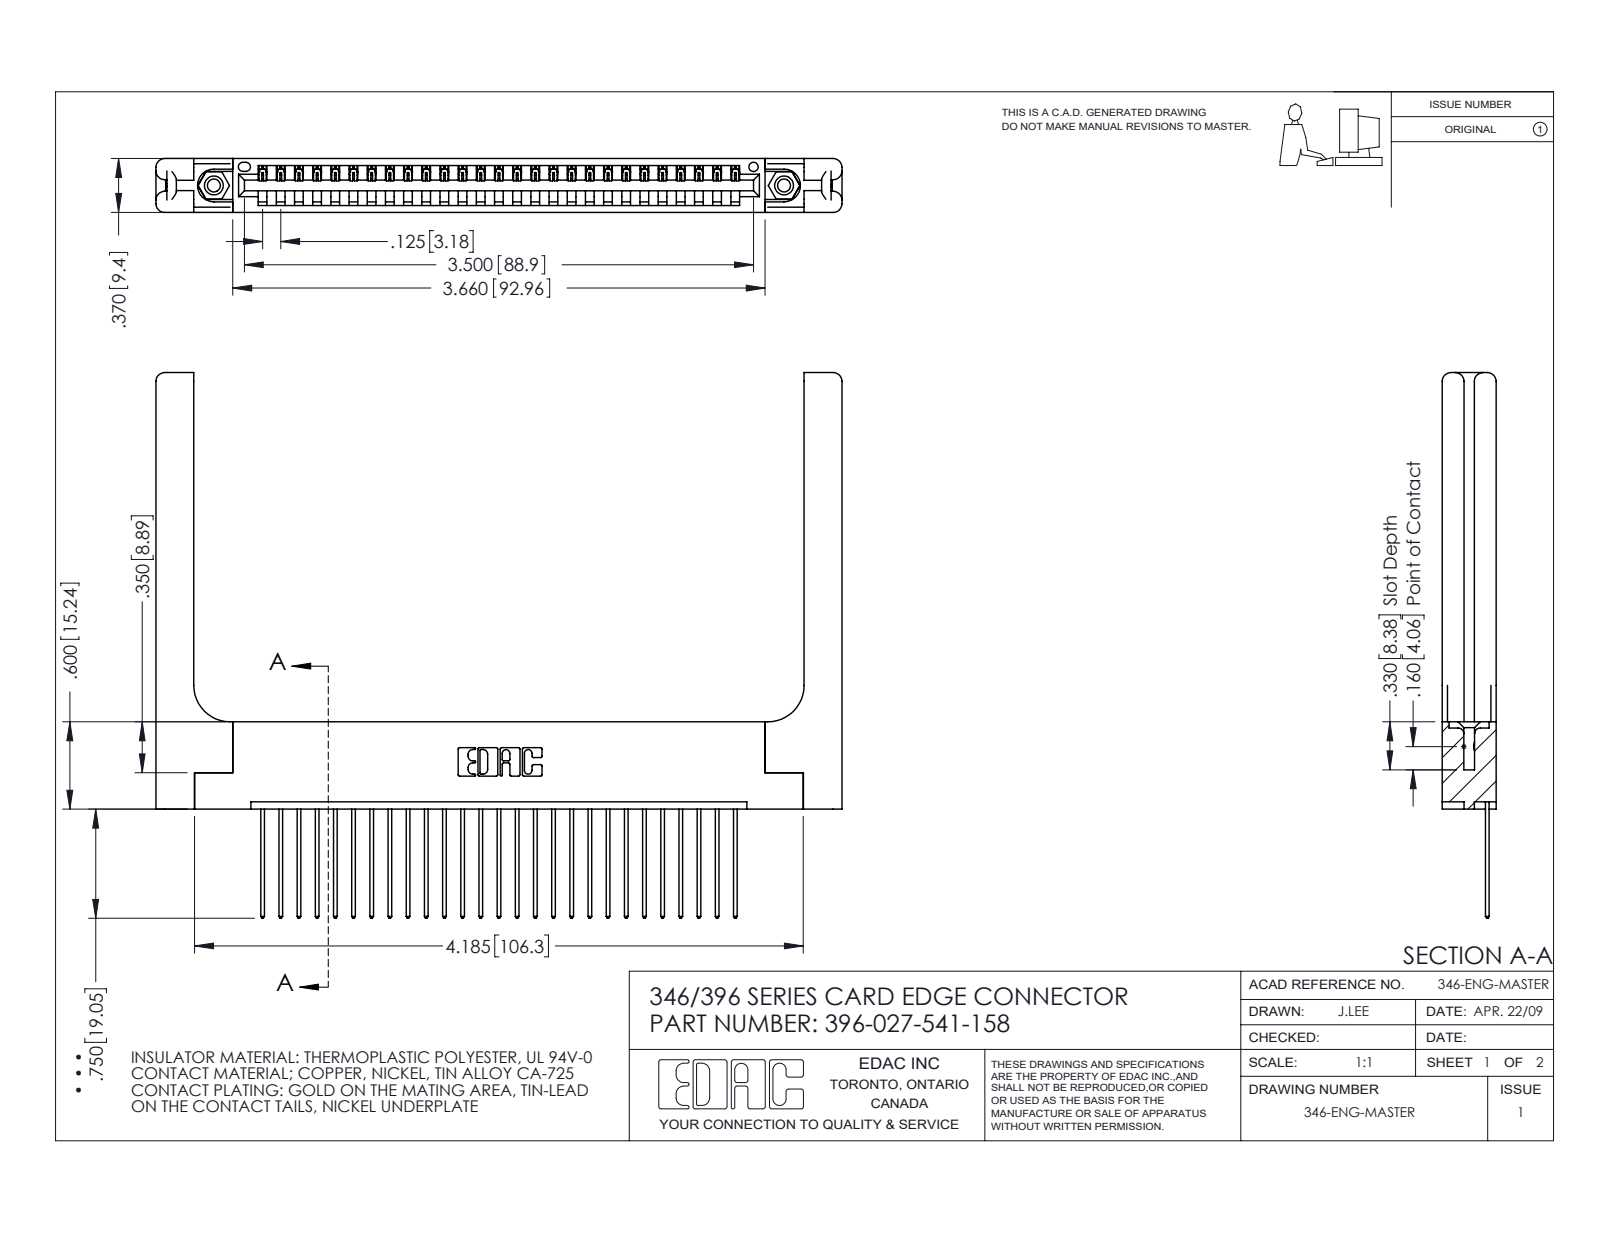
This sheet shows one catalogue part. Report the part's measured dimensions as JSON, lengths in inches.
{"part_name": "345-250-001_345-250-001-102; 396-027-541-158; 345-292-001_345-293-141; 346 Part_Flush Mounting Lugs - 0.156 Dia-TH (+1 more)", "step_written_by": "SolidWorks 2016 (CONFIG_CONTROL_DESIGN)", "units": "inches", "bodies": {"solids": 32, "faces": 1944, "planar": 1304, "cylindrical": 580, "other": 60}, "overall_size": [4.716, 3.75, 0.37], "volume_in3": 1.158, "surface_area_in2": 30.77, "round_holes": [[0.089, 2], [0.125, 2], [0.156, 2], [0.064, 1]], "round_bosses_or_shafts": [[0.155, 2]], "partial_cylinders_radius": [[0.006, 54], [0.01, 54], [0.01, 22], [0.06, 16], [0.007, 6], [0.031, 6], [0.026, 3], [0.03, 2]], "face_to_face_distances": [0.37, 0.072, 0.048, 0.322, 0.148, 0.15, 0.25, 0.298, 0.025, 0.076], "hole_center_spacings": [0.246, 3.712, 3.92]}
